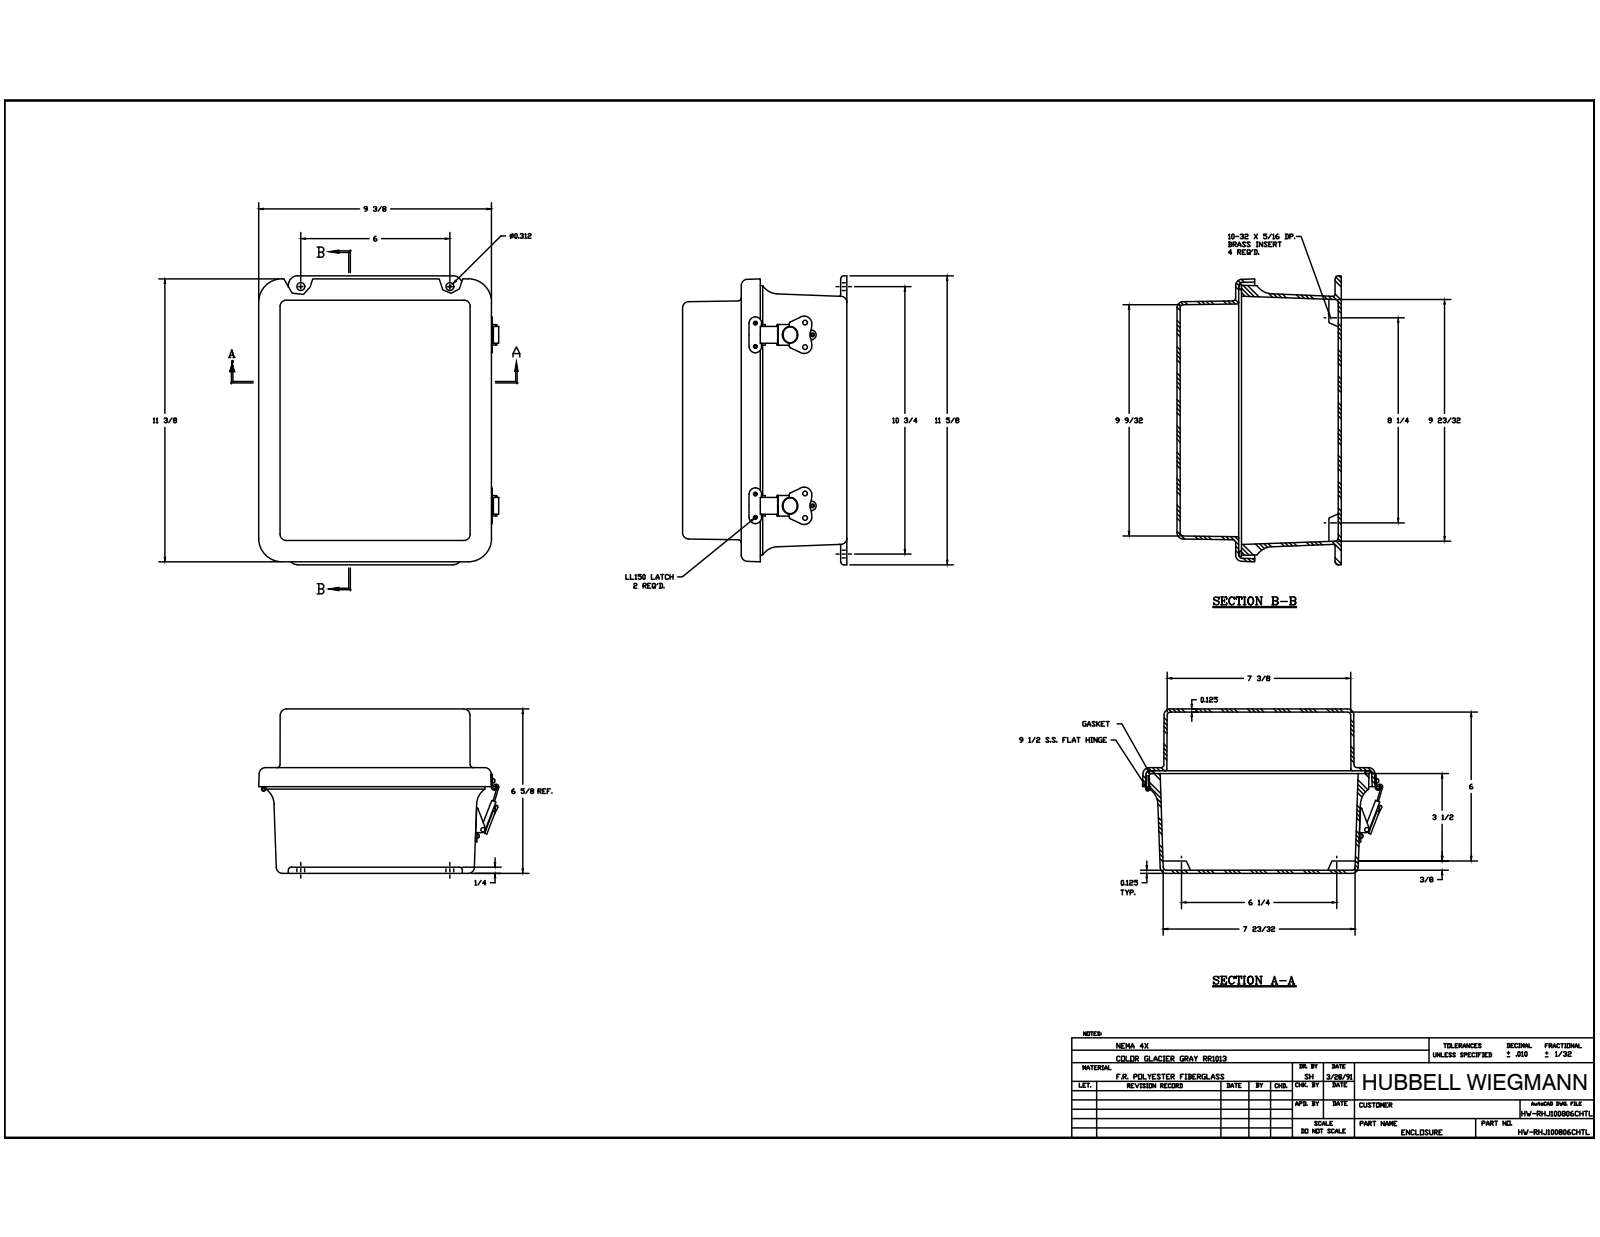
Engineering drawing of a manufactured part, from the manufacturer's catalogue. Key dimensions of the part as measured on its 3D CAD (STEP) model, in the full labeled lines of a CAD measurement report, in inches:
Part name (STEP PRODUCT): J1008HL_8; RMINS45821P_125; RMINS45821P_126; RMINS45821P_127 (+8 more)
STEP written by: Autodesk Inventor 2014 (AUTOMOTIVE_DESIGN)
Units: inches
Bodies: 48 solids, 1155 faces (499 planar, 441 cylindrical, 215 other)
Overall size (bounding box): 11.625 × 9.593 × 6.594
Volume: 69.02 in³ · Surface area: 984 in²
Round holes (diameter × count): ⌀0.14 ×16, ⌀0.131 ×8, ⌀0.152 ×5, ⌀0.13 ×4, ⌀0.156 ×4, ⌀0.165 ×4, ⌀0.197 ×4, ⌀0.218 ×4, ⌀0.118 ×2, ⌀0.138 ×2, ⌀0.181 ×2, ⌀0.182 ×2
Round bosses / shafts (diameter × count): ⌀0.25 ×16, ⌀0.125 ×16, ⌀0.27 ×4, ⌀0.583 ×2, ⌀0.524 ×2, ⌀0.209 ×2, ⌀0.185 ×2, ⌀0.128 ×2
Partial cylindrical surfaces — rounded edges, fillets, slot ends (radius × count): R0.125 ×24, R0.031 ×20, R0.079 ×20, R0.25 ×12, R0.037 ×8, R0.039 ×8, R0.045 ×8, R0.047 ×8
Main face-to-face distances: 0.125, 0.125, 6.344, 6.469, 6.594, 6.469, 4.109, 3.984, 2.36, 2.485
Hole centre spacings: 7, 6, 3, 0.25, 0.701, 0.826, 0.938, 1.337
